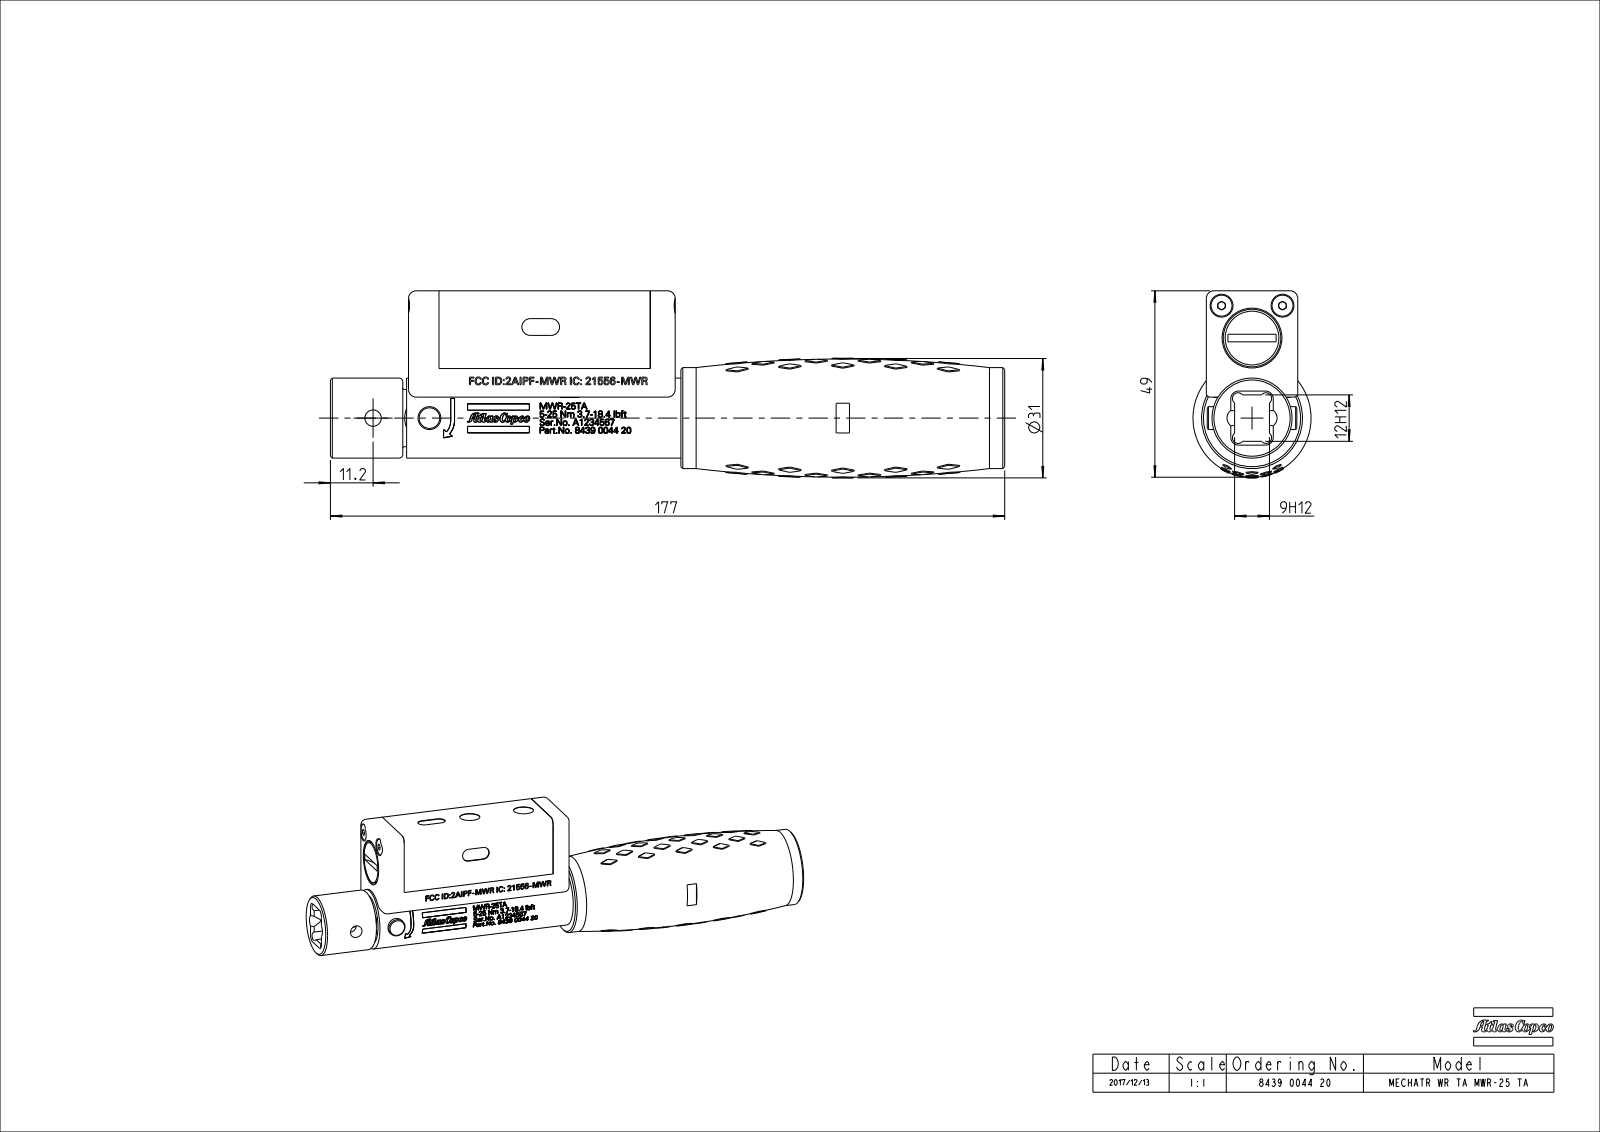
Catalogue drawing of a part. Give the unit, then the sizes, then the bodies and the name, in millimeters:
Units: millimetres
Overall size (bounding box): 177 × 49.21 × 31
Round holes (diameter × count): ⌀6 ×2, ⌀7 ×2, ⌀4.3 ×1, ⌀10.5 ×1, ⌀15.1 ×1, ⌀16.7 ×1, ⌀26.5 ×1
Round bosses / shafts (diameter × count): ⌀5.5 ×2, ⌀21 ×1, ⌀15 ×1, ⌀14.1 ×1, ⌀6 ×1
Partial cylindrical surfaces — rounded edges, fillets, slot ends (radius × count): R2 ×8, R0.5 ×6, R0.4 ×4, R2.25 ×4, R1 ×2, R11 ×1
Main face-to-face distances: 24, 55.45, 8, 8.05, 63.45, 63.5, 27.9, 6.5, 62, 16.5
Hole centre spacings: 11.67, 30.57, 16, 20, 21
Bodies: 0 solids, 605 faces (88 planar, 82 cylindrical, 435 other)
Part name (STEP PRODUCT): 8439004420
STEP written by: SolidWorks 2016 (AUTOMOTIVE_DESIGN)
